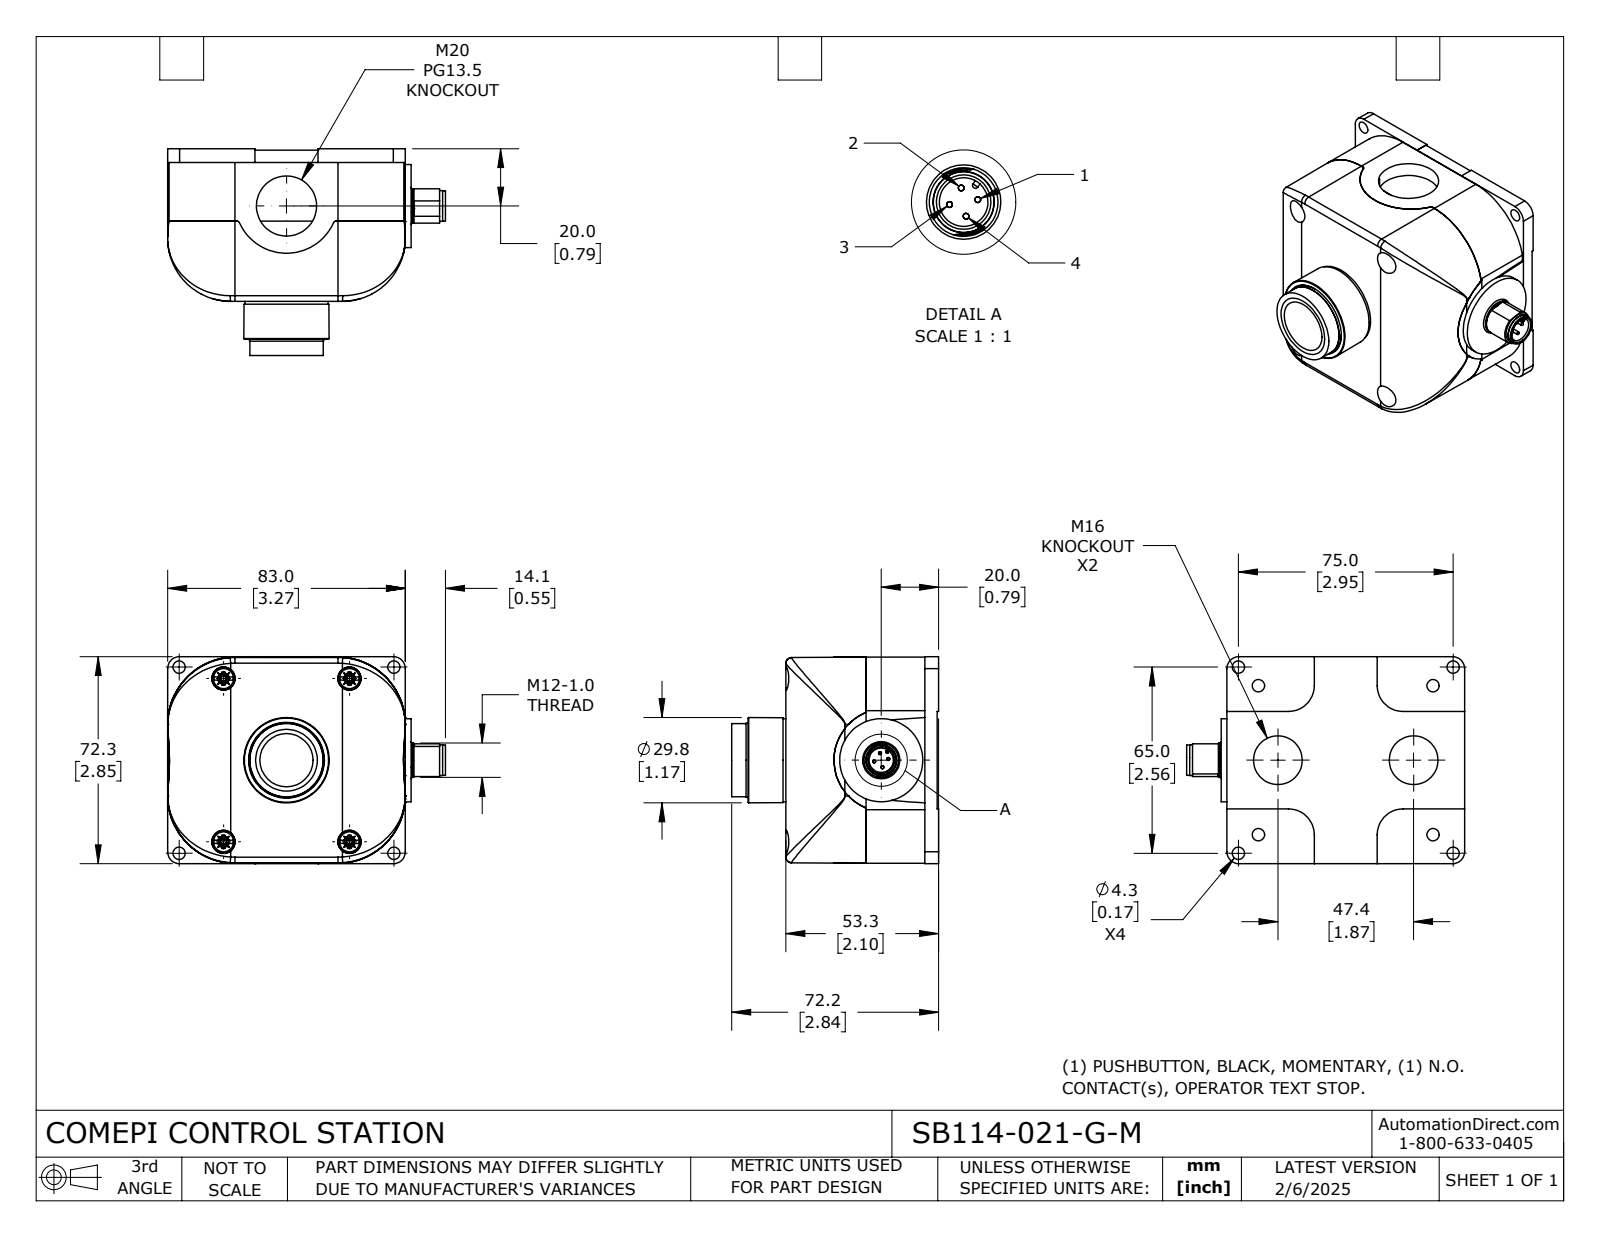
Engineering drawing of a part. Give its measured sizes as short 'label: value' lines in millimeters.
name: SB114-021-G-M
written by: SolidWorks 2024 (CONFIG_CONTROL_DESIGN)
unit: mm
bodies: 5 solids, 769 faces (362 planar, 265 cylindrical, 142 other)
size: 97.1 × 72.3 × 72.2
volume: 219 800 mm³; area: 61 950 mm²
holes: 8× ⌀4.3, 4× ⌀1, 4× ⌀1, 4× ⌀1.7, 4× ⌀2.2, 4× ⌀8.2, 2× ⌀17, 2× ⌀21, 1× ⌀8.5, 1× ⌀13.5, 1× ⌀18.1, 1× ⌀21.7
bosses: 4× ⌀7, 4× ⌀2.2, 4× ⌀1.7, 2× ⌀29, 2× ⌀0.6, 1× ⌀26.4, 1× ⌀25.9, 1× ⌀25.6
rounds: 5× R0.5, 4× R0.9, 4× R2, 4× R9, 4× R9.7, 4× R23.5, 2× R0.2, 2× R0.3
face distances: 24.8, 2.5, 22.3, 52.8, 50.3, 28, 3, 53.3, 0.5, 25.3
hole spacings: 9.6, 26.9, 35.3, 40.1, 49.6, 58.9, 60.1, 68.3
